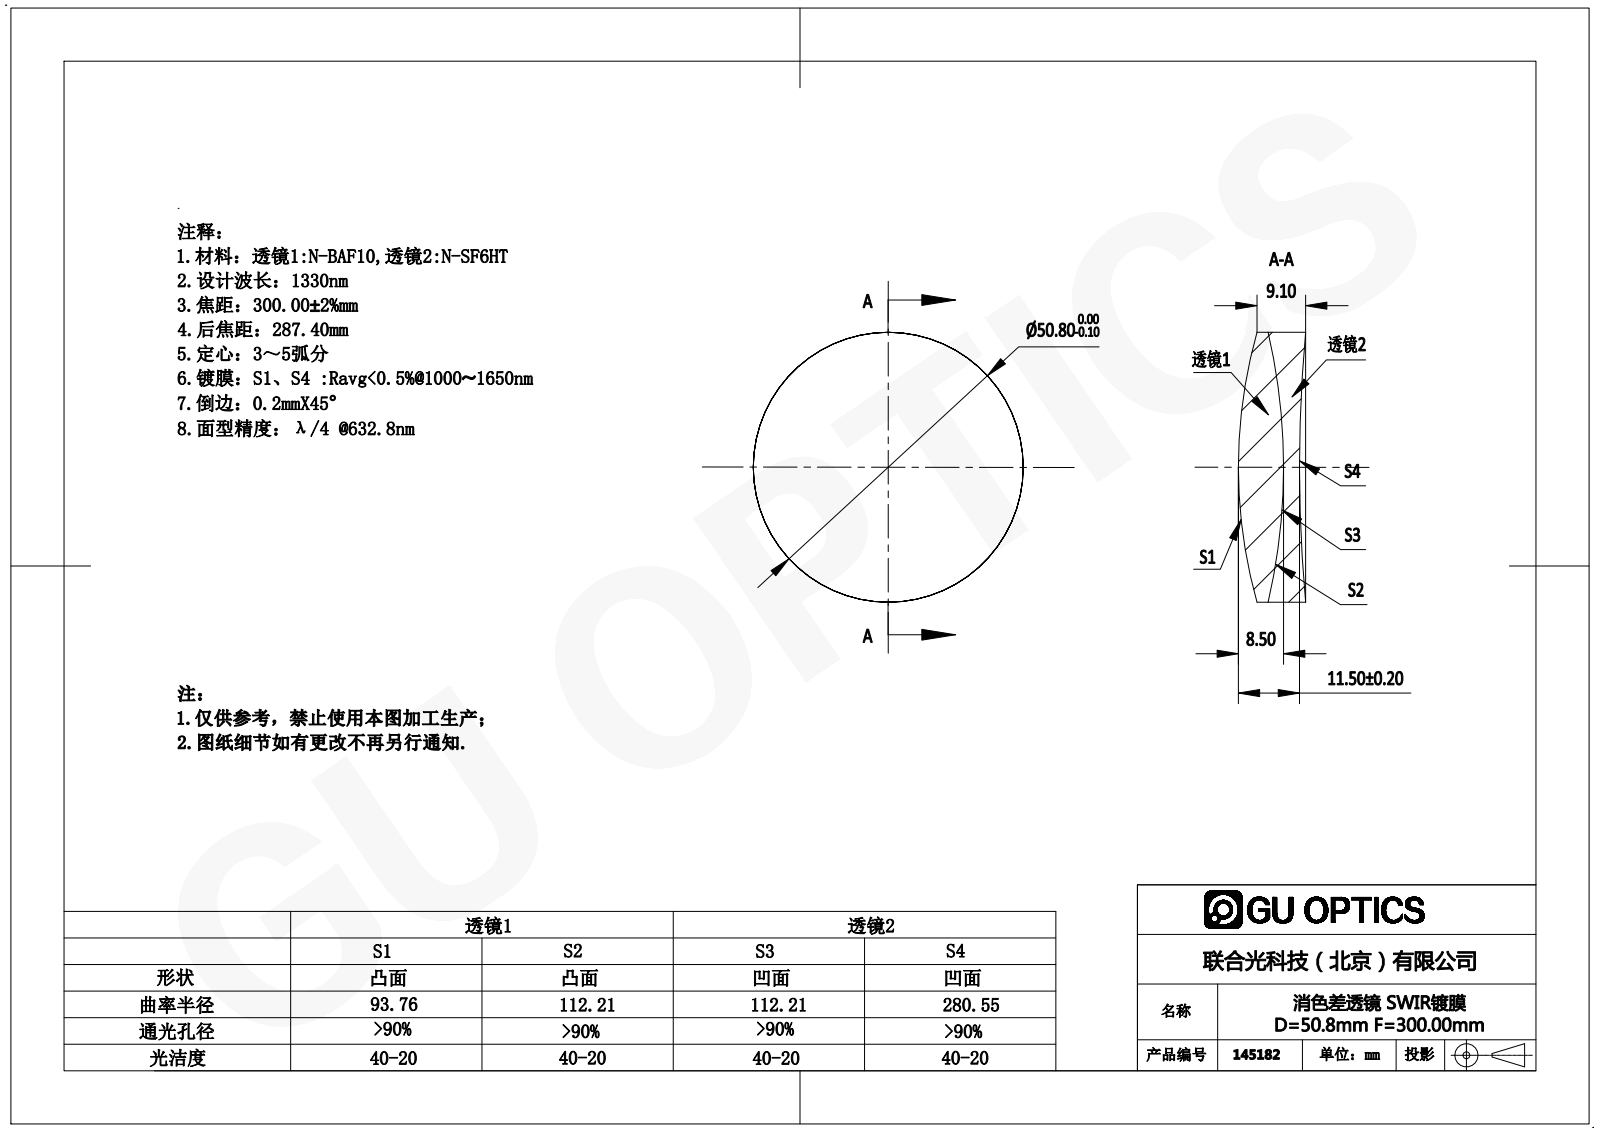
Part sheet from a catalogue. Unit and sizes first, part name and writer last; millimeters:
Units: millimetres
Overall size (bounding box): 50.8 × 50.8 × 12.65
Round bosses / shafts (diameter × count): ⌀50.8 ×1
Volume: 20 945 mm³ · Surface area: 9 663 mm²
Bodies: 2 solids, 12 faces (0 planar, 4 cylindrical, 8 other)
Part name (STEP PRODUCT): 145182
STEP written by: SolidWorks 2016 (AUTOMOTIVE_DESIGN)
